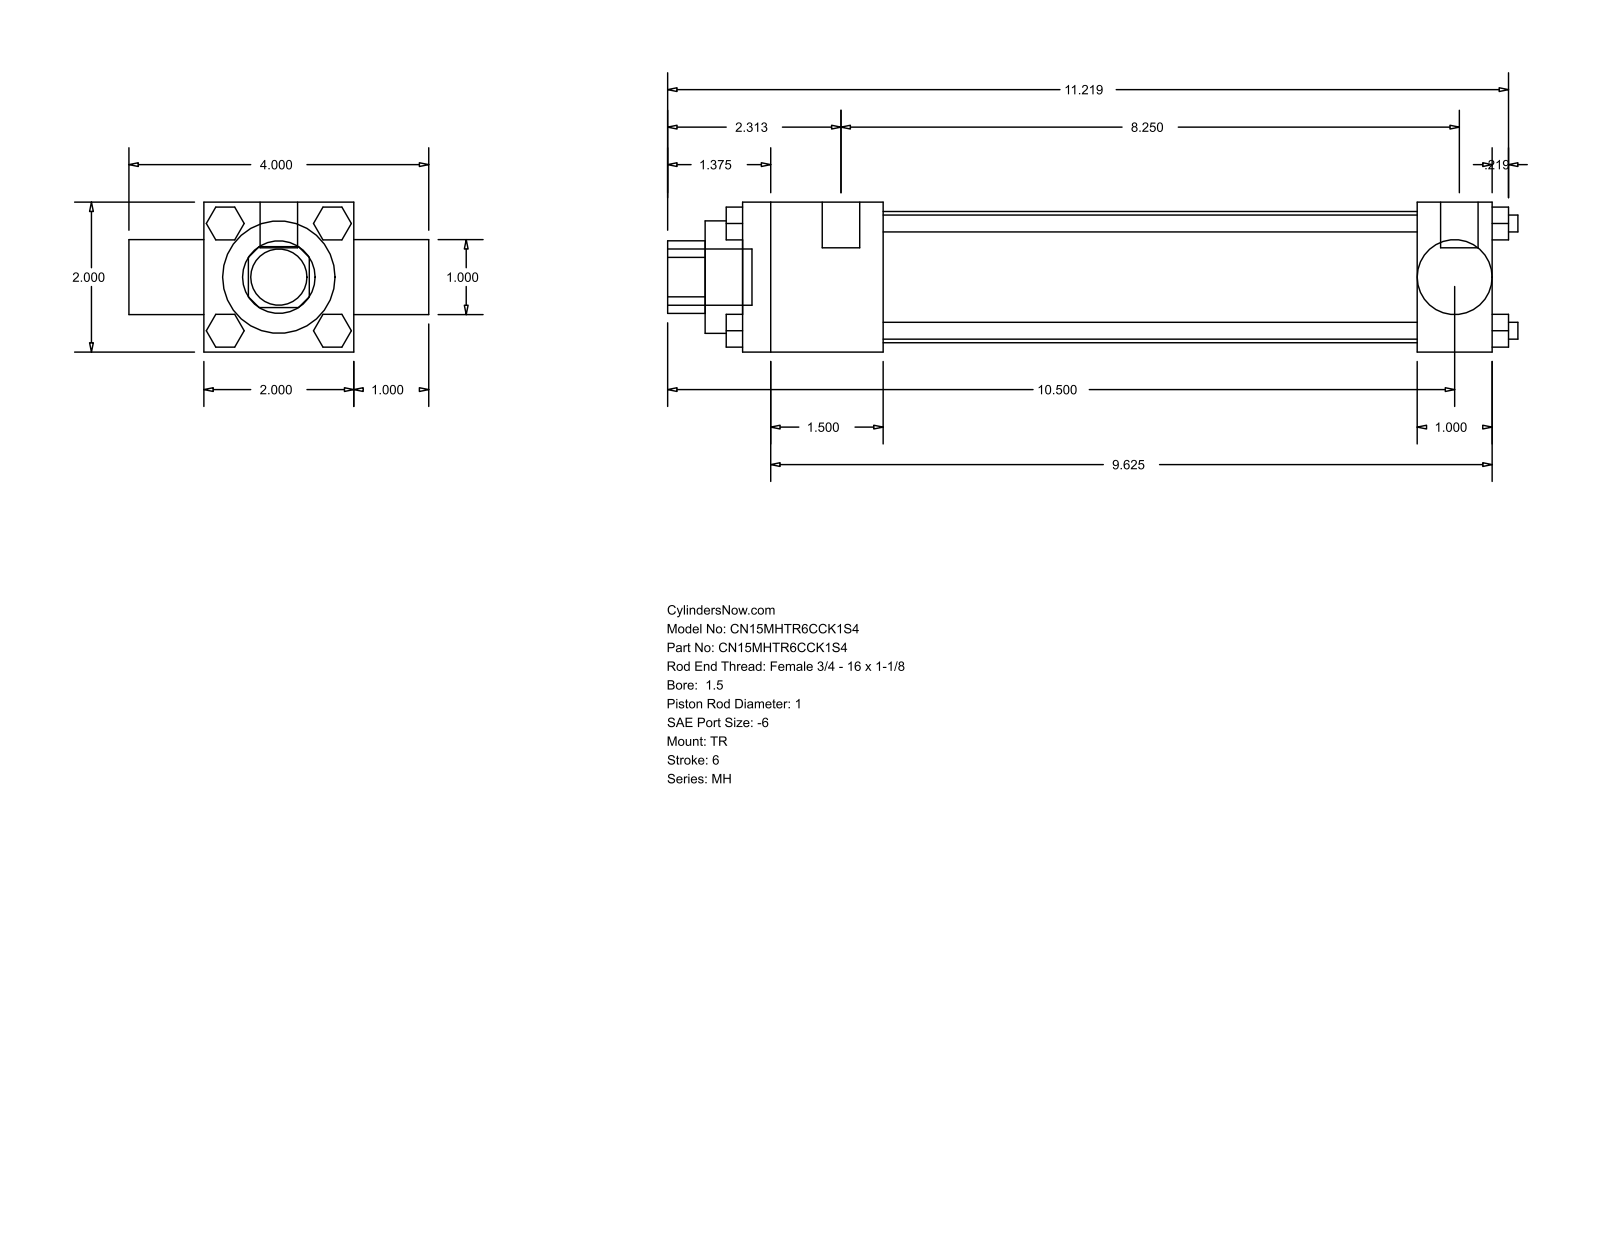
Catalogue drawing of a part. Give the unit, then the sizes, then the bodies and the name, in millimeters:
Units: millimetres
Overall size (bounding box): 288.13 × 101.6 × 50.8
Round holes (diameter × count): ⌀25.35 ×1, ⌀25.4 ×1, ⌀38.1 ×1, ⌀44.45 ×1
Round bosses / shafts (diameter × count): ⌀5.71 ×4, ⌀5.56 ×3, ⌀12.7 ×2, ⌀19.05 ×1
Partial cylindrical surfaces — rounded edges, fillets, slot ends (radius × count): R12.29 ×1
Main face-to-face distances: 50.8, 25.4, 254, 76.2, 47.63, 206.37, 228.6, 180.97, 259.56, 12.7
Bodies: 0 solids, 120 faces (92 planar, 28 cylindrical, 0 other)
Part name (STEP PRODUCT): MH_TR__0150_1
STEP written by: GSSL Pune (CONFIG_CONTROL_DESIGN)
